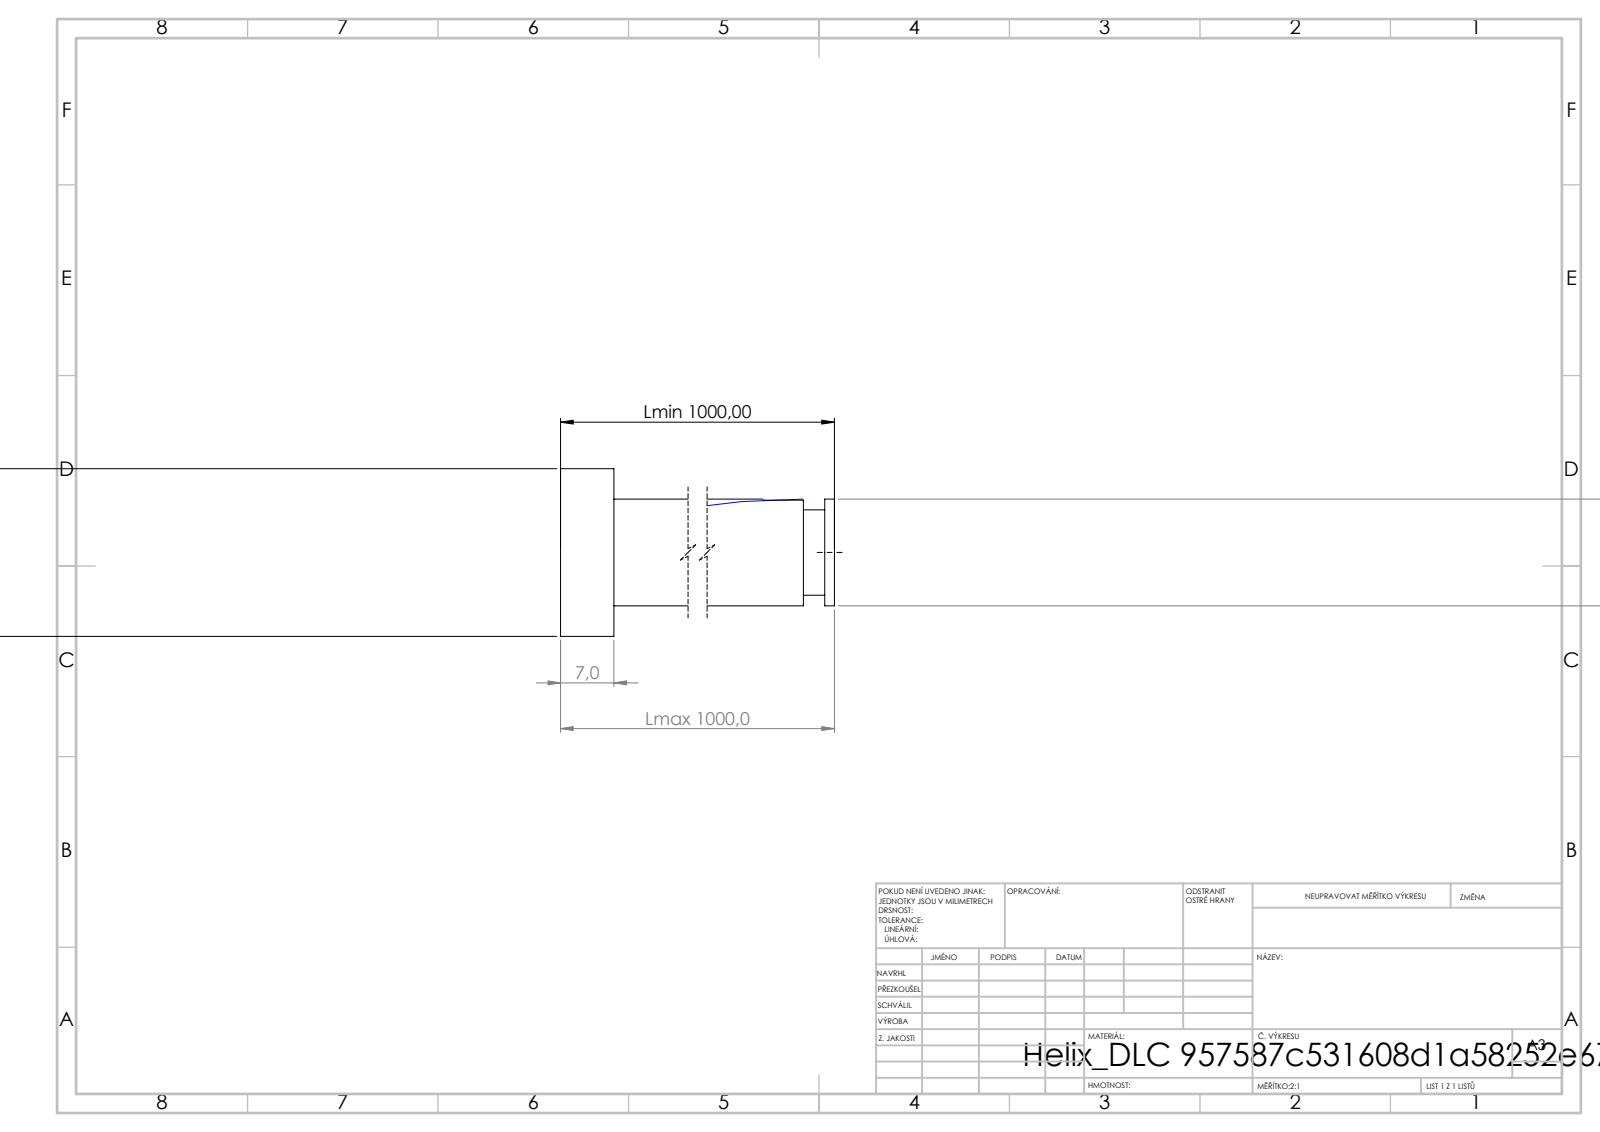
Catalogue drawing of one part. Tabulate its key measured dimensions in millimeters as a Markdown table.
| quantity | value |
| --- | --- |
| STEP written by | SolidWorks 2019 (CONFIG_CONTROL_DESIGN) |
| units | millimeters |
| bodies | 1 solid, 16 faces (6 planar, 9 cylindrical, 1 other) |
| overall size | 1000 × 22 × 22 |
| volume | 188 102 mm³ |
| surface area | 60 356 mm² |
| round bosses / shafts (diameter × count) | 22 × 1, 14 × 1, 11.2 × 1 |
| main face-to-face distances | 7, 1000, 993, 998.72, 991.72, 1.28, 995.92, 988.92, 2.8, 4.08 |
